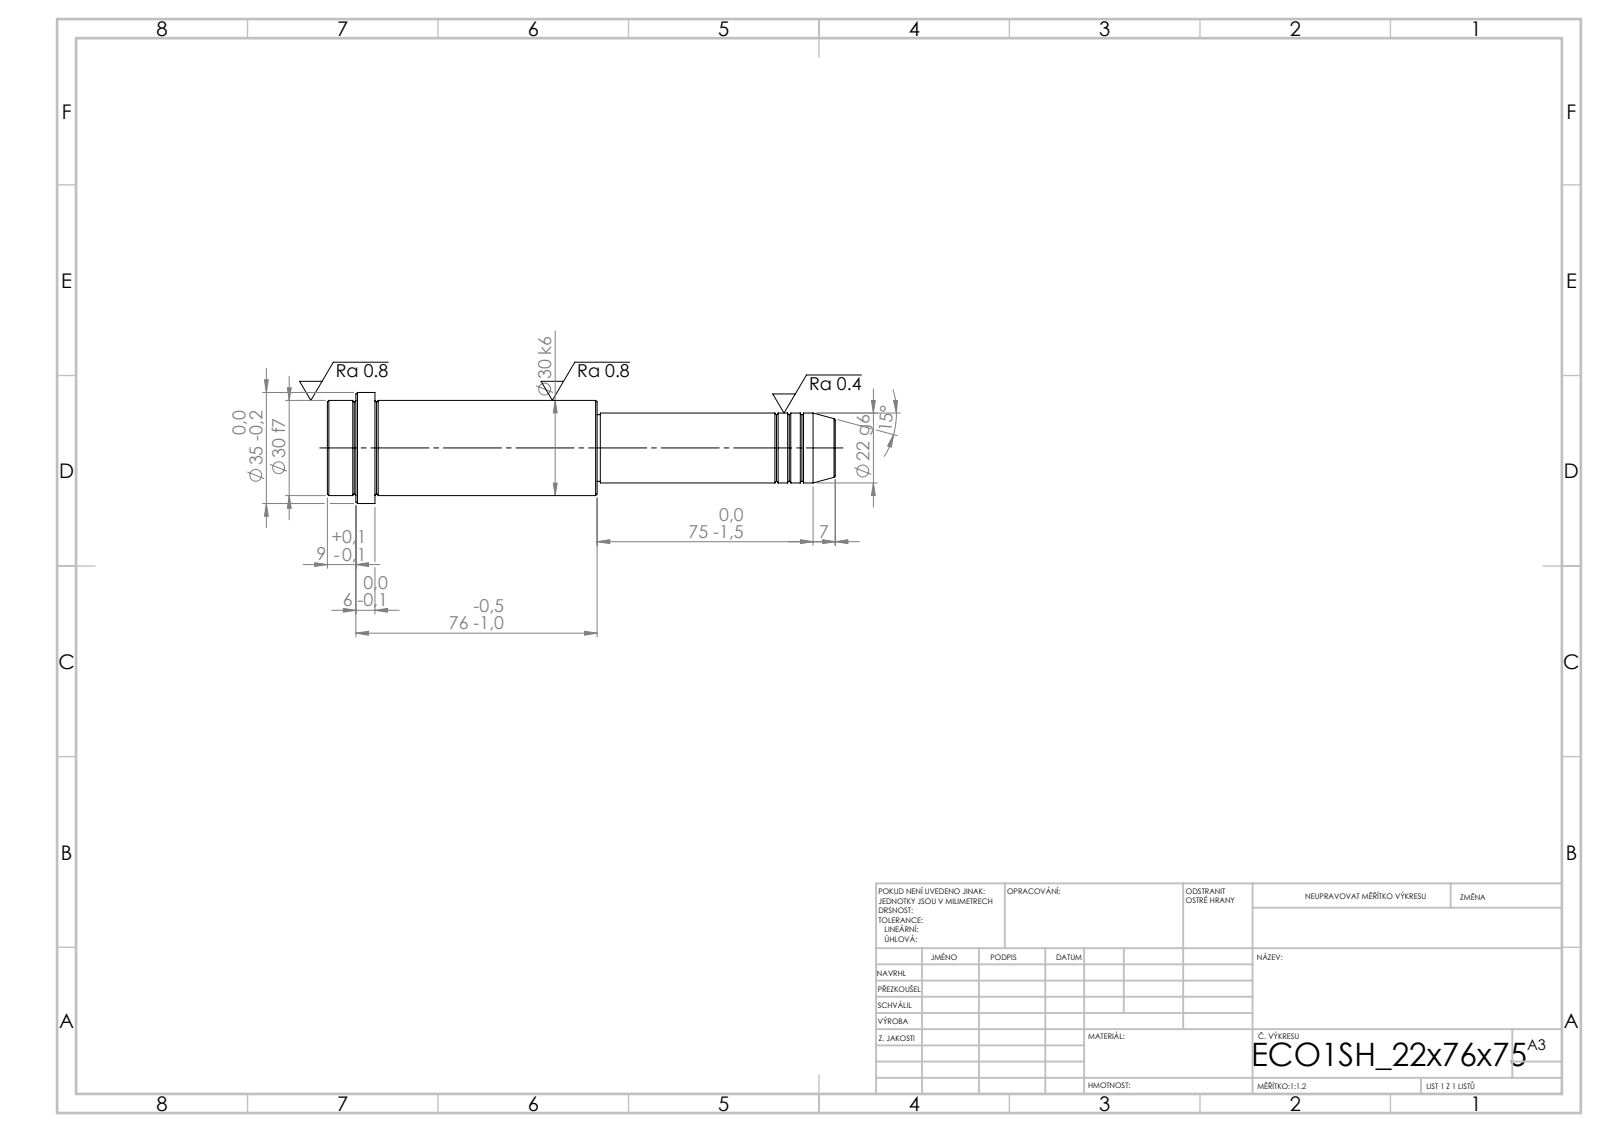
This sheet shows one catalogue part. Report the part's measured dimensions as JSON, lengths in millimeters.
{"step_written_by": "SolidWorks 2019 (CONFIG_CONTROL_DESIGN)", "units": "millimeters", "bodies": {"solids": 1, "faces": 52, "planar": 6, "cylindrical": 16, "other": 30}, "overall_size": [160, 35, 35], "volume_mm3": 89471, "surface_area_mm2": 15249, "round_bosses_or_shafts": [[35, 1], [30, 1], [22, 1], [21, 1]], "face_to_face_distances": [85, 70, 15, 75, 145, 160, 151, 76, 6, 9]}
